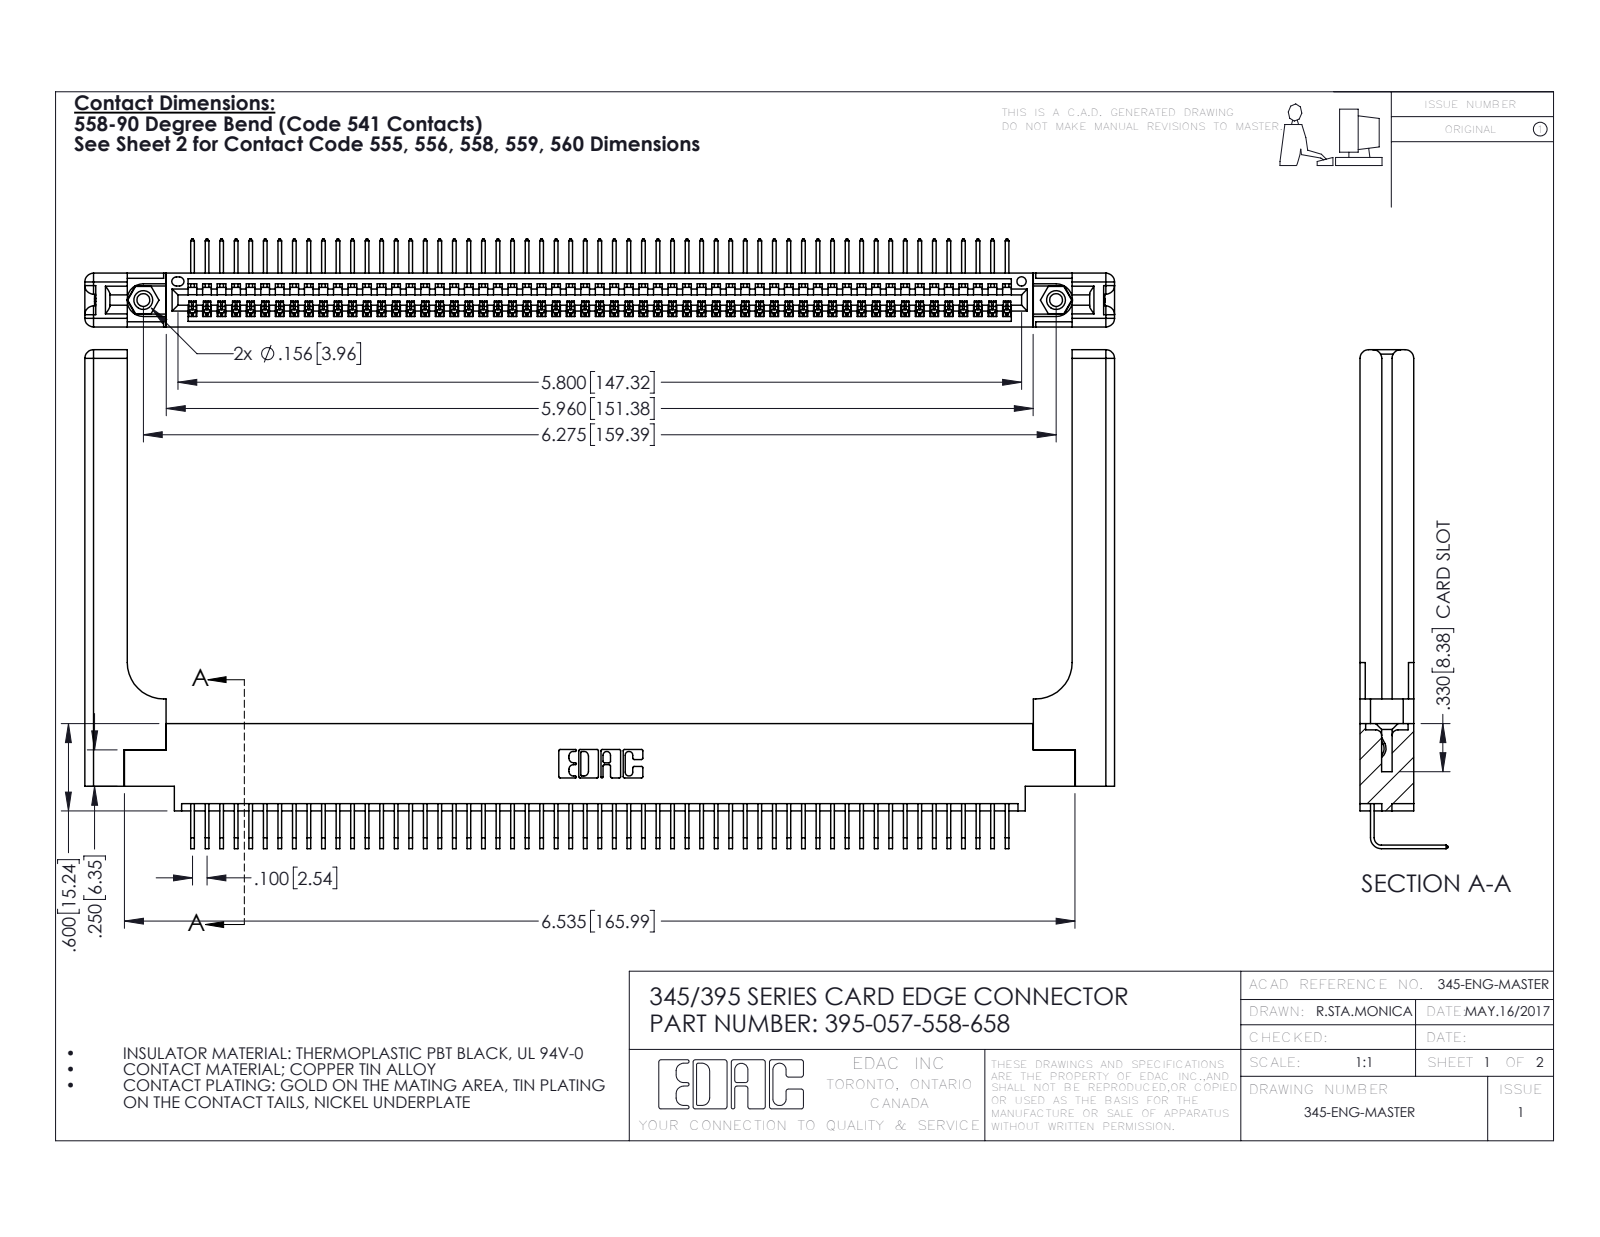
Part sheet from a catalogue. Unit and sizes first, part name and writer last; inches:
Units: inches
Overall size (bounding box): 7.079 × 3.429 × 0.605
Round holes (diameter × count): ⌀0.089 ×2, ⌀0.125 ×2, ⌀0.156 ×2, ⌀0.064 ×1
Round bosses / shafts (diameter × count): ⌀0.155 ×2
Partial cylindrical surfaces — rounded edges, fillets, slot ends (radius × count): R0.006 ×114, R0.01 ×22, R0.06 ×16, R0.007 ×6, R0.031 ×6, R0.026 ×3, R0.03 ×2, R0.031 ×2
Main face-to-face distances: 0.072, 0.37, 0.298, 0.098, 0.272, 0.025, 0.2, 0.225, 0.148, 0.15
Hole centre spacings: 0.27, 6.039, 6.275
Volume: 1.573 in³ · Surface area: 46.05 in²
Bodies: 62 solids, 3806 faces (2626 planar, 1120 cylindrical, 60 other)
Part name (STEP PRODUCT): 345 Part_0.170 Offset - 0.156 Dia-TH; 345-250-001_345-250-001-102; 395-057-558-658; 345-292-001_558 Tail - 2 (+1 more)
STEP written by: SolidWorks 2016 (CONFIG_CONTROL_DESIGN)
